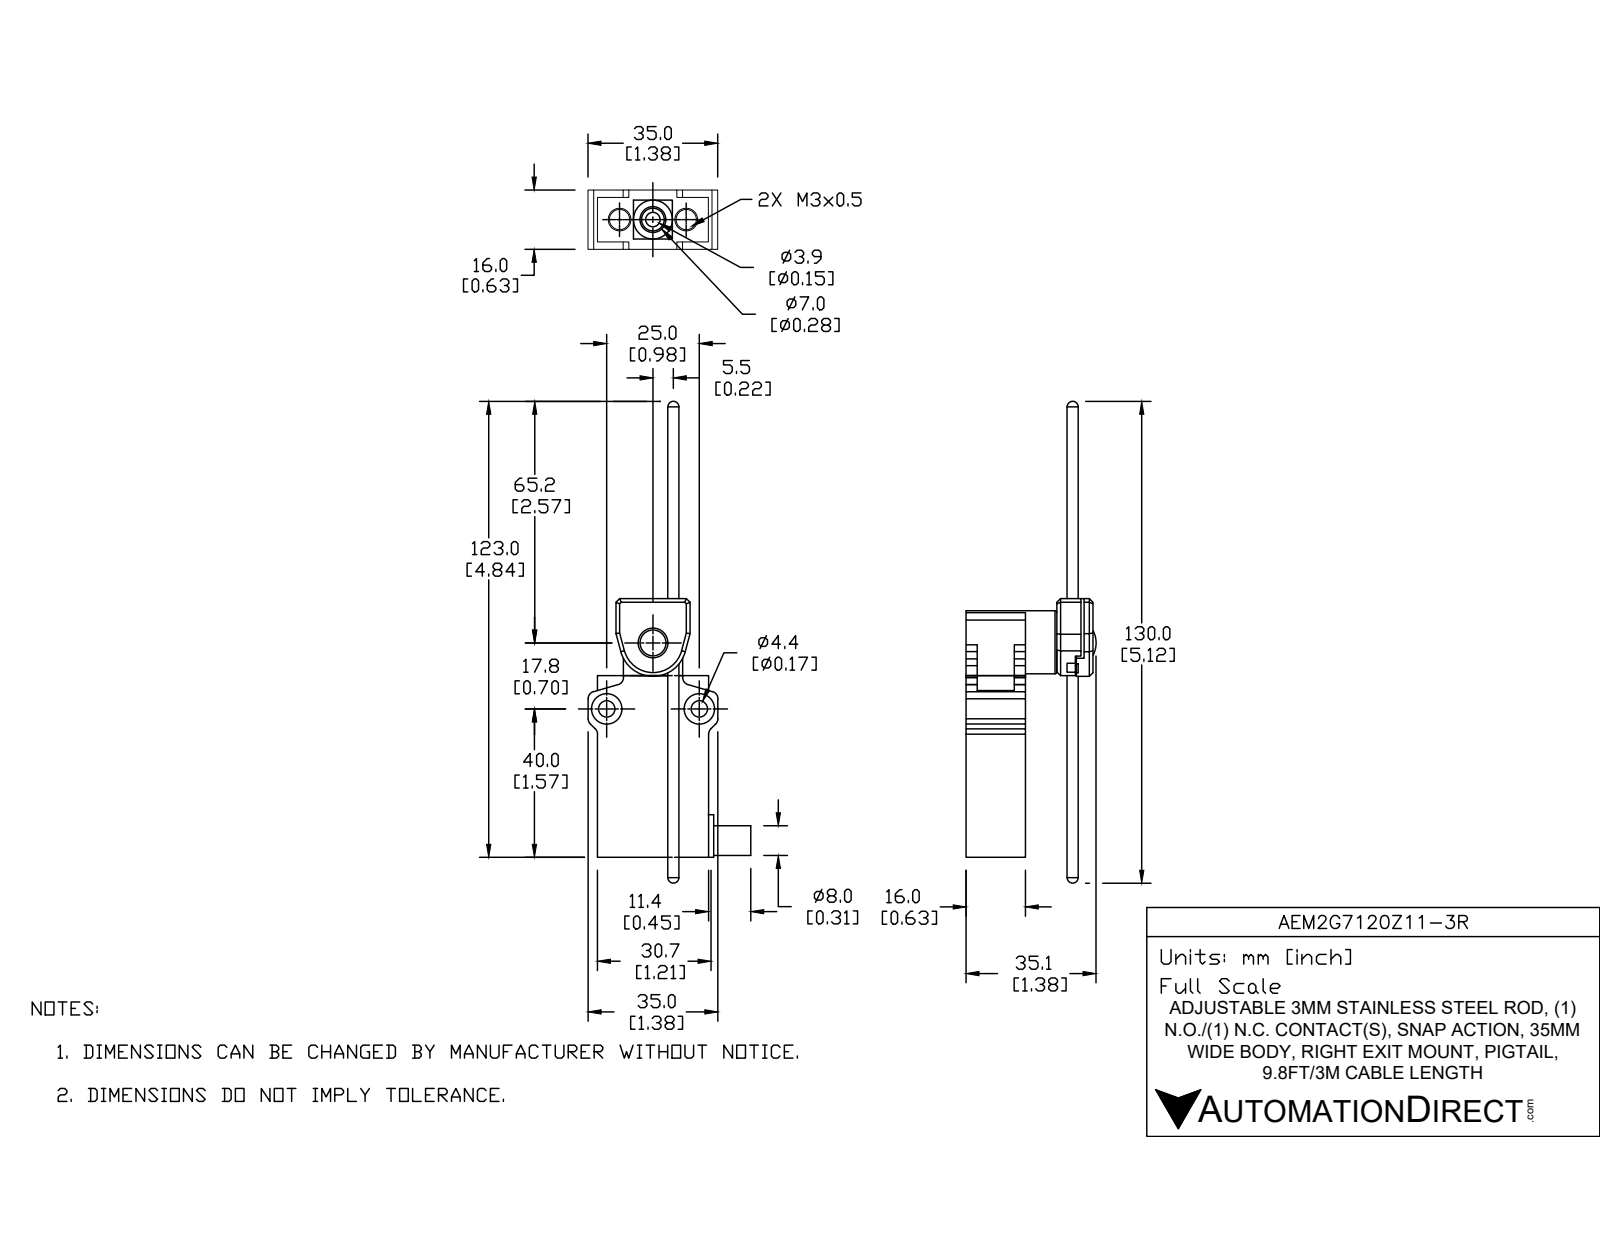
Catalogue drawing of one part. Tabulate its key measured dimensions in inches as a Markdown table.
| quantity | value |
| --- | --- |
| part name | AEM2G7120Z11-3R |
| STEP written by | SolidWorks 2017 (AUTOMOTIVE_DESIGN) |
| units | inches |
| bodies | 7 solids, 221 faces (139 planar, 65 cylindrical, 17 other) |
| overall size | 6.803 × 1.87 × 1.366 |
| volume | 1.945 in³ |
| surface area | 20.49 in² |
| round holes (diameter × count) | 0.118 × 2, 0.173 × 2, 0.323 × 2, 0.138 × 1, 0.197 × 1, 0.315 × 1 |
| round bosses / shafts (diameter × count) | 0.622 × 1, 0.323 × 1, 0.276 × 1, 0.118 × 1 |
| partial cylindrical surfaces (radius × count) | 0.079 × 8, 0.059 × 1, 0.173 × 1, 0.256 × 1, 0.26 × 1, 0.354 × 1 |
| main face-to-face distances | 0.63, 1.181, 1.929, 0.169, 0.472, 0.902, 0.28, 0.098, 0.697, 0.988 |
| hole center spacings | 0.863, 0.748, 0.984 |
